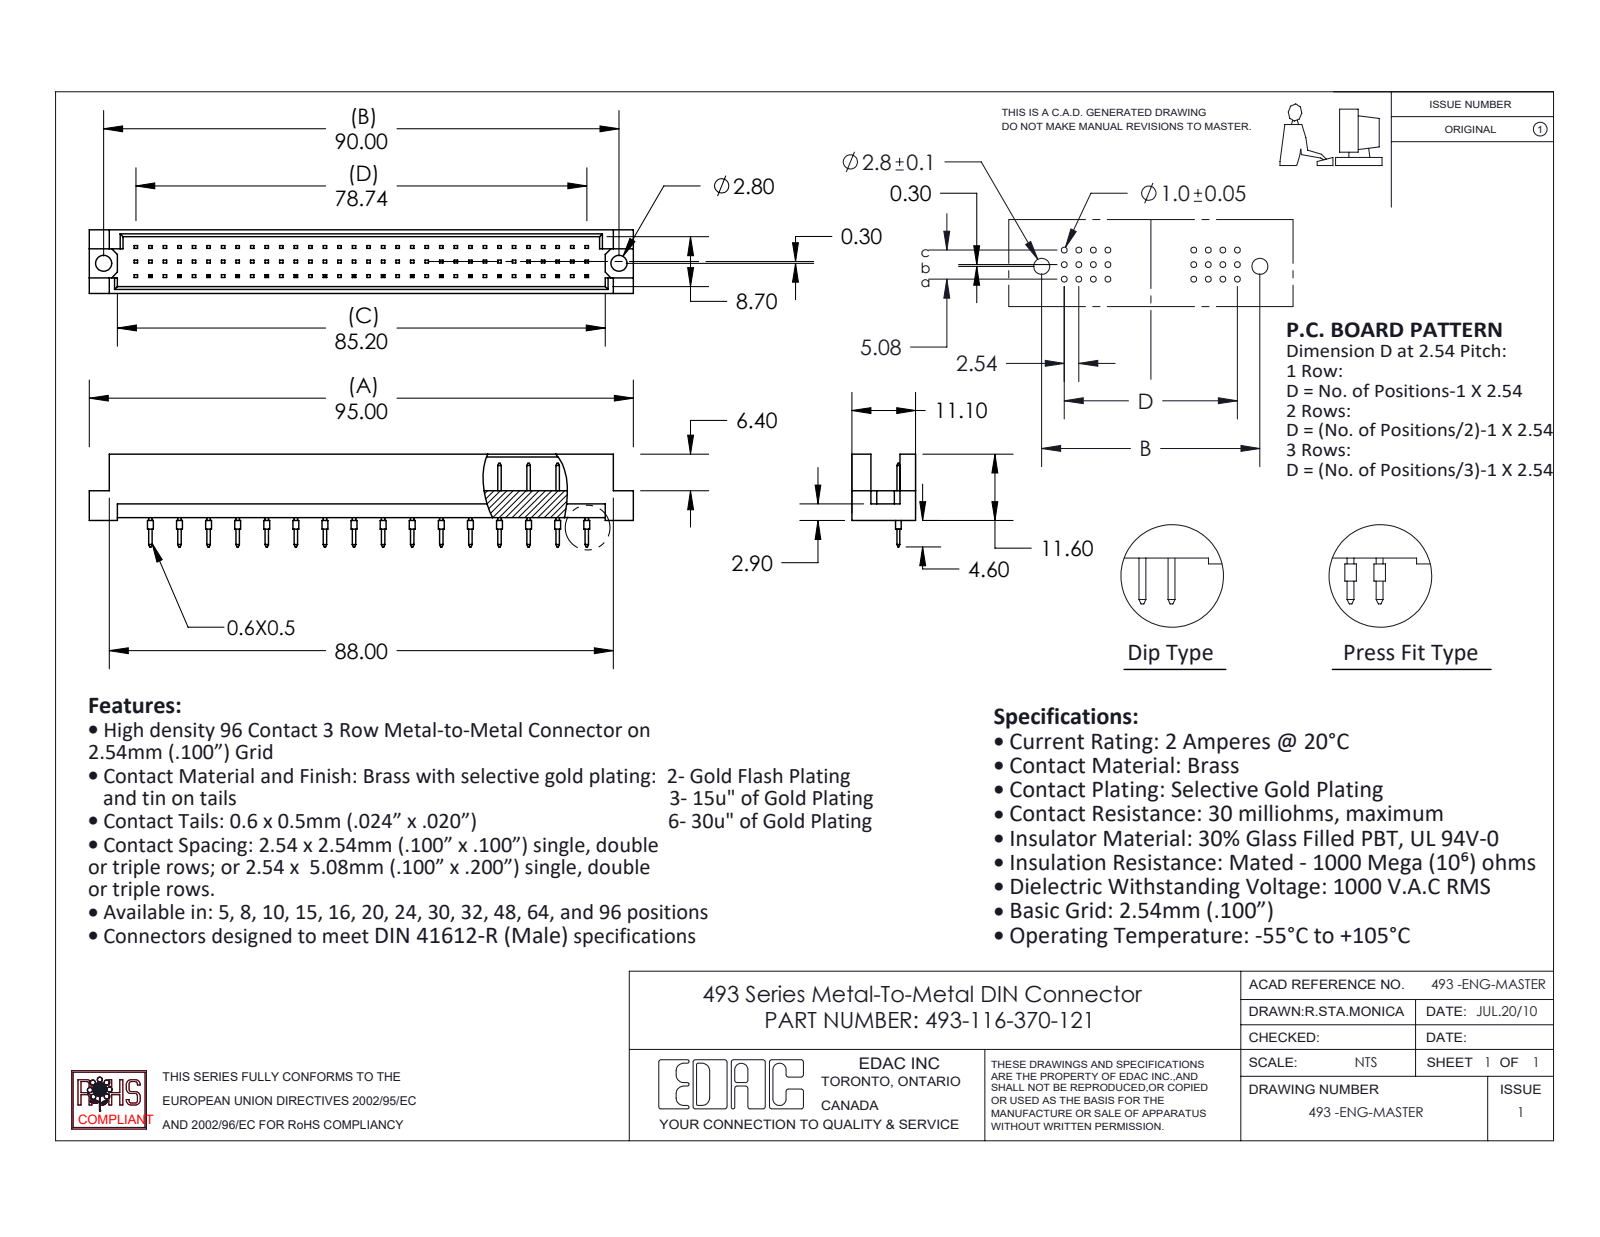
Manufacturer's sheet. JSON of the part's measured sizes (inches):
{"part_name": "493 Part_96; 493-290_70; 493-116-370-121", "step_written_by": "SolidWorks 2020 (CONFIG_CONTROL_DESIGN)", "units": "inches", "bodies": {"solids": 17, "faces": 788, "planar": 752, "cylindrical": 36, "other": 0}, "overall_size": [3.74, 0.638, 0.437], "volume_in3": 0.35, "surface_area_in2": 10.88, "round_holes": [[0.11, 2]], "round_bosses_or_shafts": [[0.039, 16]], "face_to_face_distances": [0.047, 0.39, 0.437, 0.343, 0.185, 0.02, 0.2, 0.1, 0.109, 0.128], "hole_center_spacings": [3.543]}
